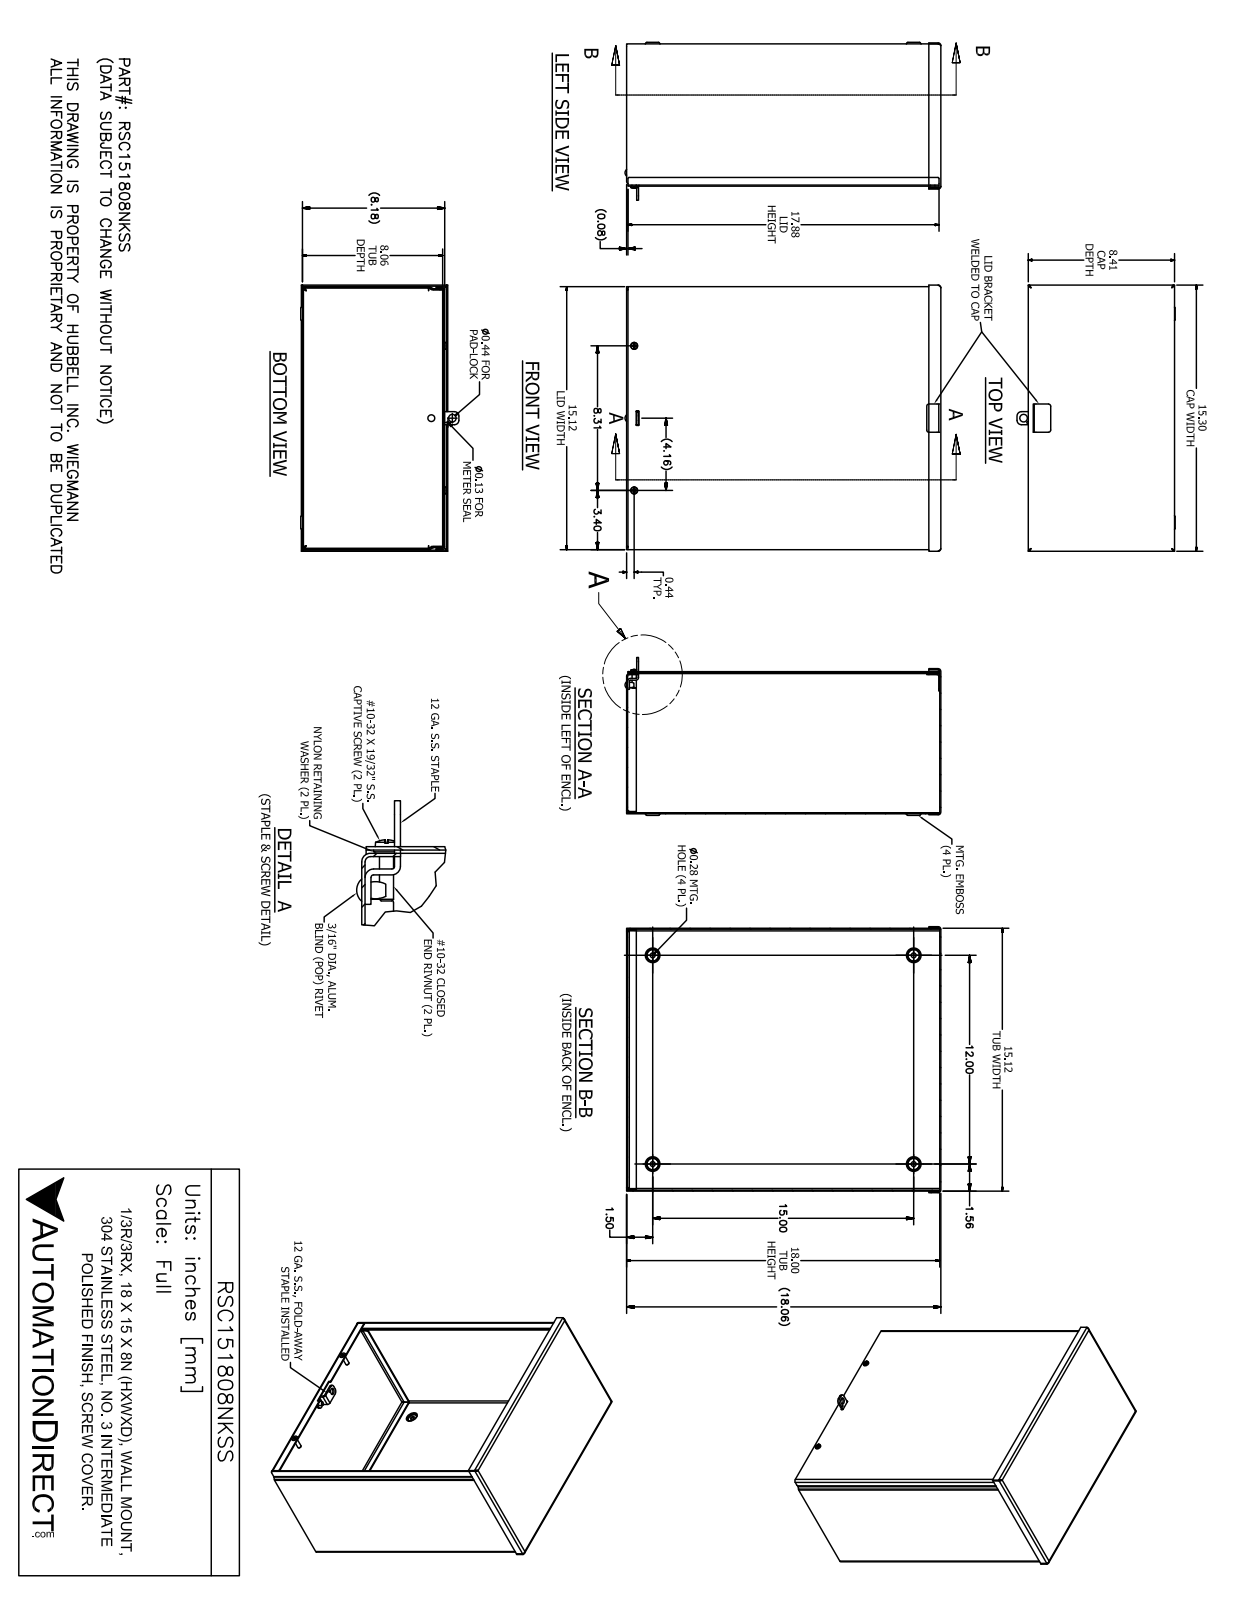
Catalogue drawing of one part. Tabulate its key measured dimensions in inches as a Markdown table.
| quantity | value |
| --- | --- |
| part name | RSC151808NKSS |
| STEP written by | SolidWorks 2017 (AUTOMOTIVE_DESIGN) |
| units | inches |
| bodies | 13 solids, 383 faces (199 planar, 99 cylindrical, 85 other) |
| overall size | 18.149 × 15.299 × 9.084 |
| volume | 67.69 in³ |
| surface area | 2 310 in² |
| round holes (diameter × count) | 0.25 × 4, 0.281 × 4, 0.156 × 2, 0.196 × 2, 0.257 × 2, 0.278 × 2, 0.125 × 1, 0.198 × 1, 0.201 × 1, 0.437 × 1 |
| round bosses / shafts (diameter × count) | 0.453 × 2, 0.406 × 2, 0.248 × 2, 0.167 × 2, 0.187 × 1 |
| partial cylindrical surfaces (radius × count) | 0.094 × 17, 0.153 × 17, 0.031 × 6, 0.125 × 4, 0.25 × 4, 0.047 × 2, 0.05 × 2, 0.062 × 2 |
| main face-to-face distances | 0.059, 8.117, 8.176, 15.059, 8.058, 18, 15, 15.118, 18.059, 17.941 |
| hole center spacings | 2.128, 2.144, 8.313, 10.212, 10.215, 12, 15, 16.168 |
